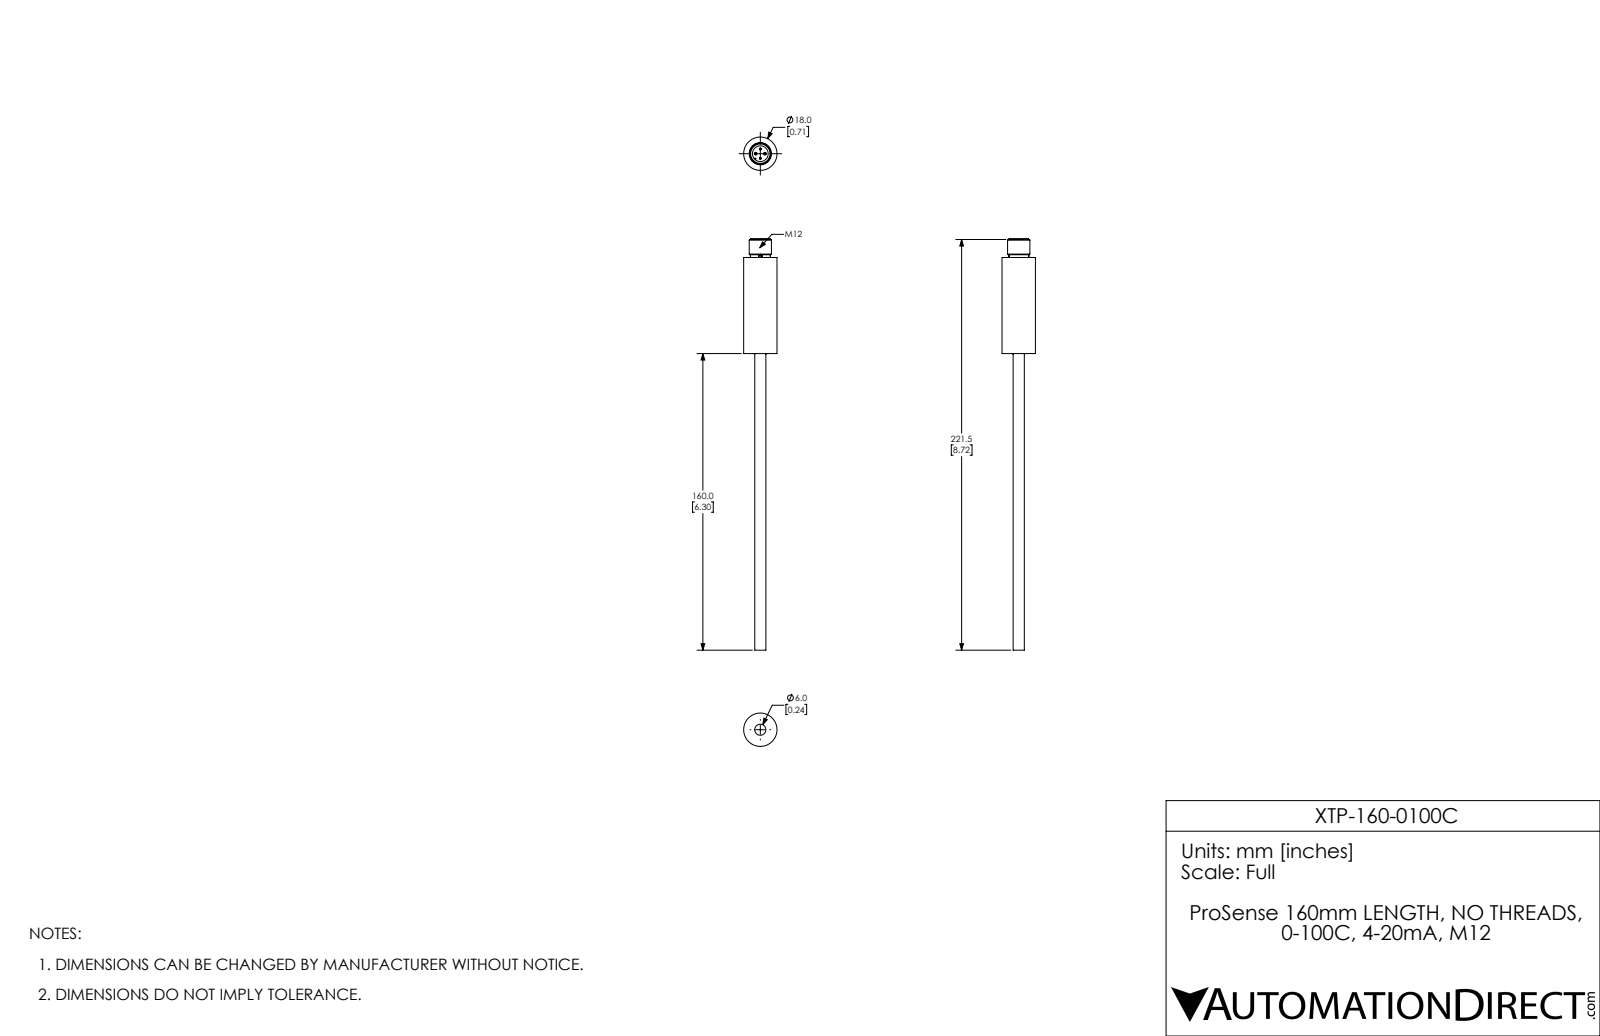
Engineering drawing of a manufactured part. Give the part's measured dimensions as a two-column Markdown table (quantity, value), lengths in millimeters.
| quantity | value |
| --- | --- |
| part name | XTP-160-0100C |
| STEP written by | SolidWorks 2017 (AUTOMOTIVE_DESIGN) |
| units | millimeters |
| bodies | 1 solid, 67 faces (24 planar, 21 cylindrical, 22 other) |
| overall size | 222 × 18 × 18 |
| volume | 18 320 mm³ |
| surface area | 7 155 mm² |
| round holes (diameter × count) | 8.5 × 1 |
| round bosses / shafts (diameter × count) | 1 × 4, 18 × 1, 12 × 1, 10.7 × 1, 10.5 × 1, 6 × 1 |
| partial cylindrical surfaces (radius × count) | 0.4 × 1 |
| main face-to-face distances | 51.8, 53, 1.2, 62, 10.2, 9, 160, 211.8, 213, 222 |
